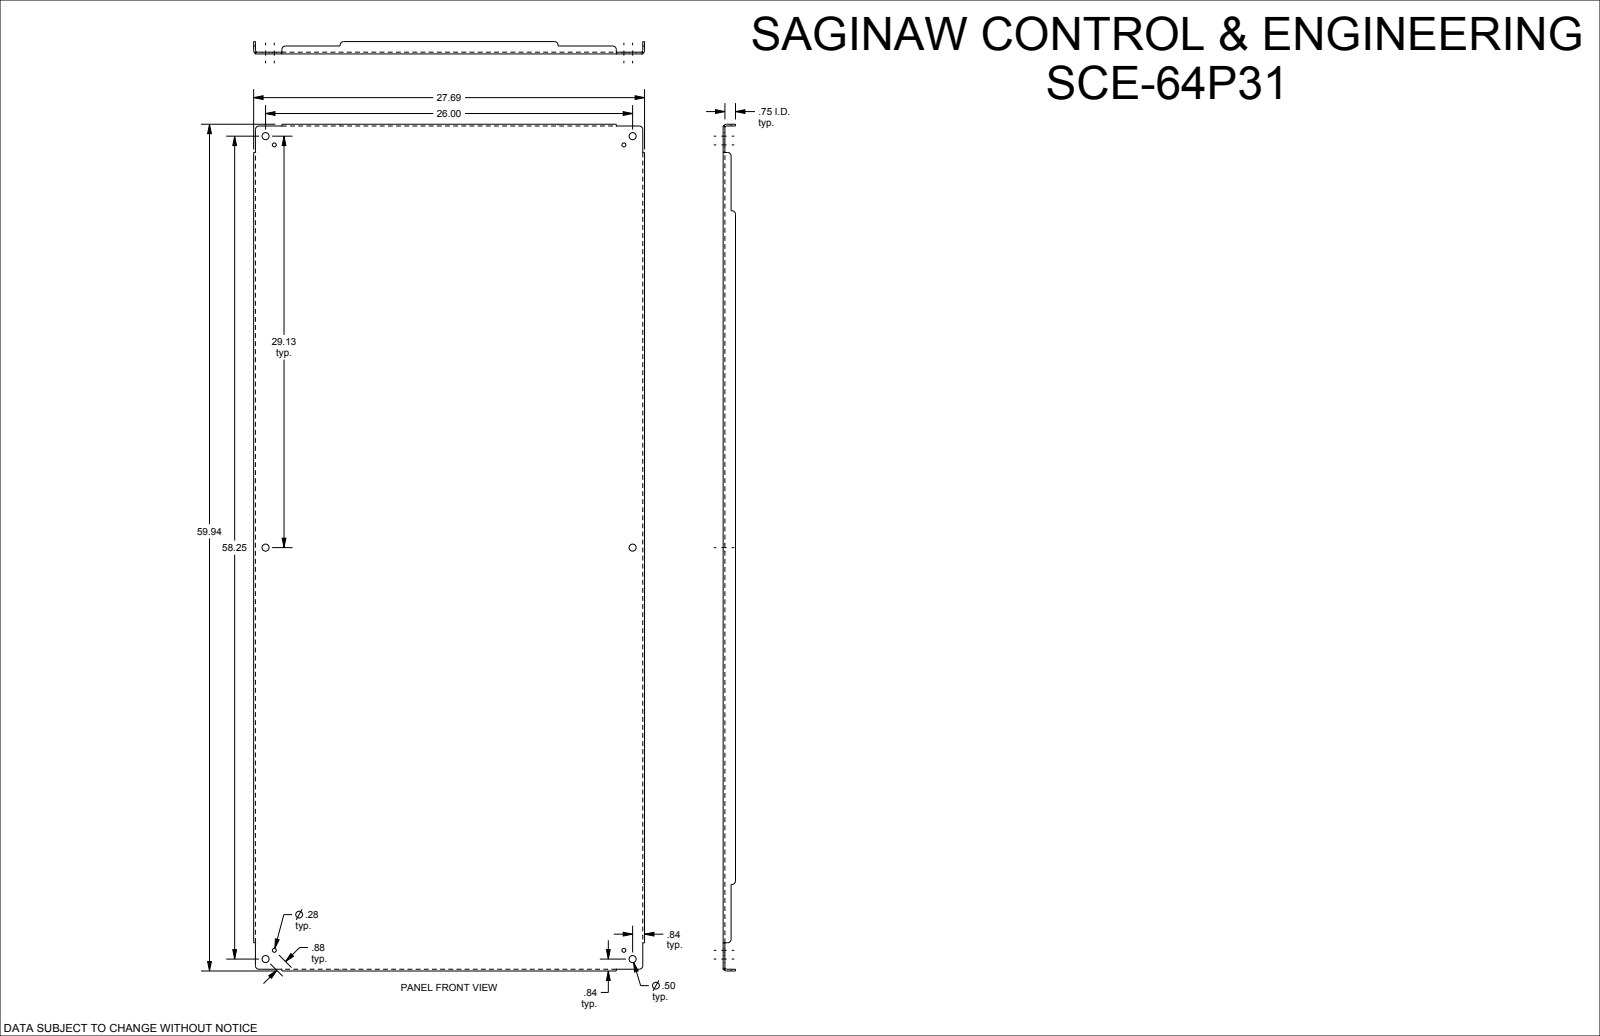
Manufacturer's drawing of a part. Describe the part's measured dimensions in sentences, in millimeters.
The part is named "SCE-64P31". Its 3-D file was written by "SolidWorks 2019 (CONFIG_CONTROL_DESIGN)". It is 1 solid with 108 faces: 46 planar, 38 cylindrical and 24 other. Overall it measures 1522.4 by 703.3 by 22.2 millimeters. Its volume is 3 590 000 cubic millimeters and its surface area 2 277 000 square millimeters. Round holes: 6 of diameter 12.7, 4 of diameter 7.1. Partial cylindrical surfaces (rounded edges, fillets, slot ends): 12 of radius 6.4, 4 of radius 2.8, 4 of radius 6. The main face-to-face distances are 3.2, 700.1, 696.9, 703.2, 3.2, 1519.3, 19.1, 22.2, 1516, 1522.4. The hole center spacings are 22.2, 644.9, 724.2, 739.8, 969.5, 991.7, 1463.9, 1599.5.
